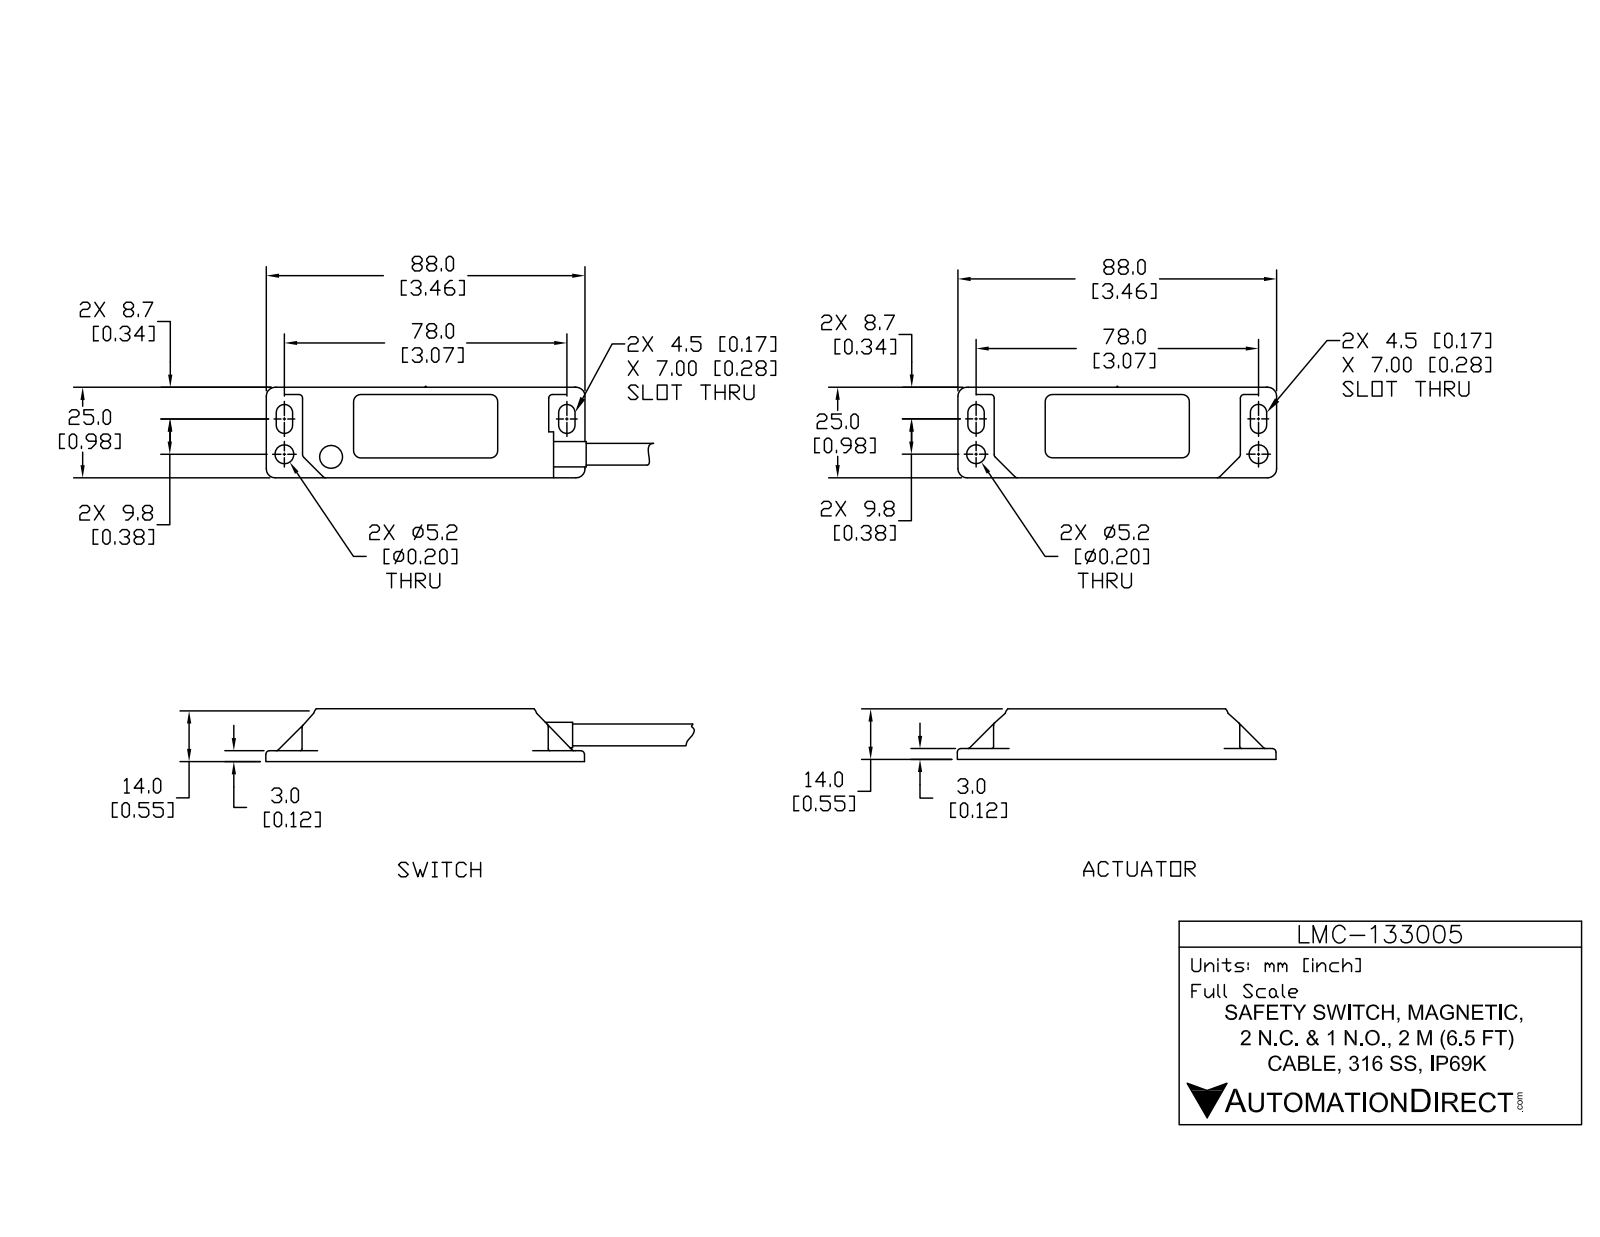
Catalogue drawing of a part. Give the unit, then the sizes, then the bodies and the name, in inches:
Units: inches
Overall size (bounding box): 9.186 × 2.008 × 0.551
Round holes (diameter × count): ⌀0.197 ×4, ⌀0.213 ×4, ⌀0.232 ×1, ⌀0.283 ×1
Round bosses / shafts (diameter × count): ⌀0.079 ×4, ⌀0.193 ×2, ⌀0.134 ×2, ⌀0.339 ×1, ⌀0.299 ×1, ⌀0.28 ×1, ⌀0.236 ×1
Partial cylindrical surfaces — rounded edges, fillets, slot ends (radius × count): R0.02 ×95, R0.039 ×45, R0.091 ×8, R0.098 ×4, R0.256 ×4, R0.193 ×1
Main face-to-face distances: 0.067, 0.055, 0.543, 1.024, 0.476, 0.488, 0.421, 0.917, 0.106, 0.039
Hole centre spacings: 0.67, 1.172, 1.181, 1.243, 1.496, 1.687, 1.815, 1.907
Volume: 1.66 in³ · Surface area: 46.34 in²
Bodies: 10 solids, 676 faces (194 planar, 244 cylindrical, 238 other)
Part name (STEP PRODUCT): LMC-133005; LMC-133005_2; LMC-133005_1
STEP written by: SolidWorks 2017 (AUTOMOTIVE_DESIGN)
